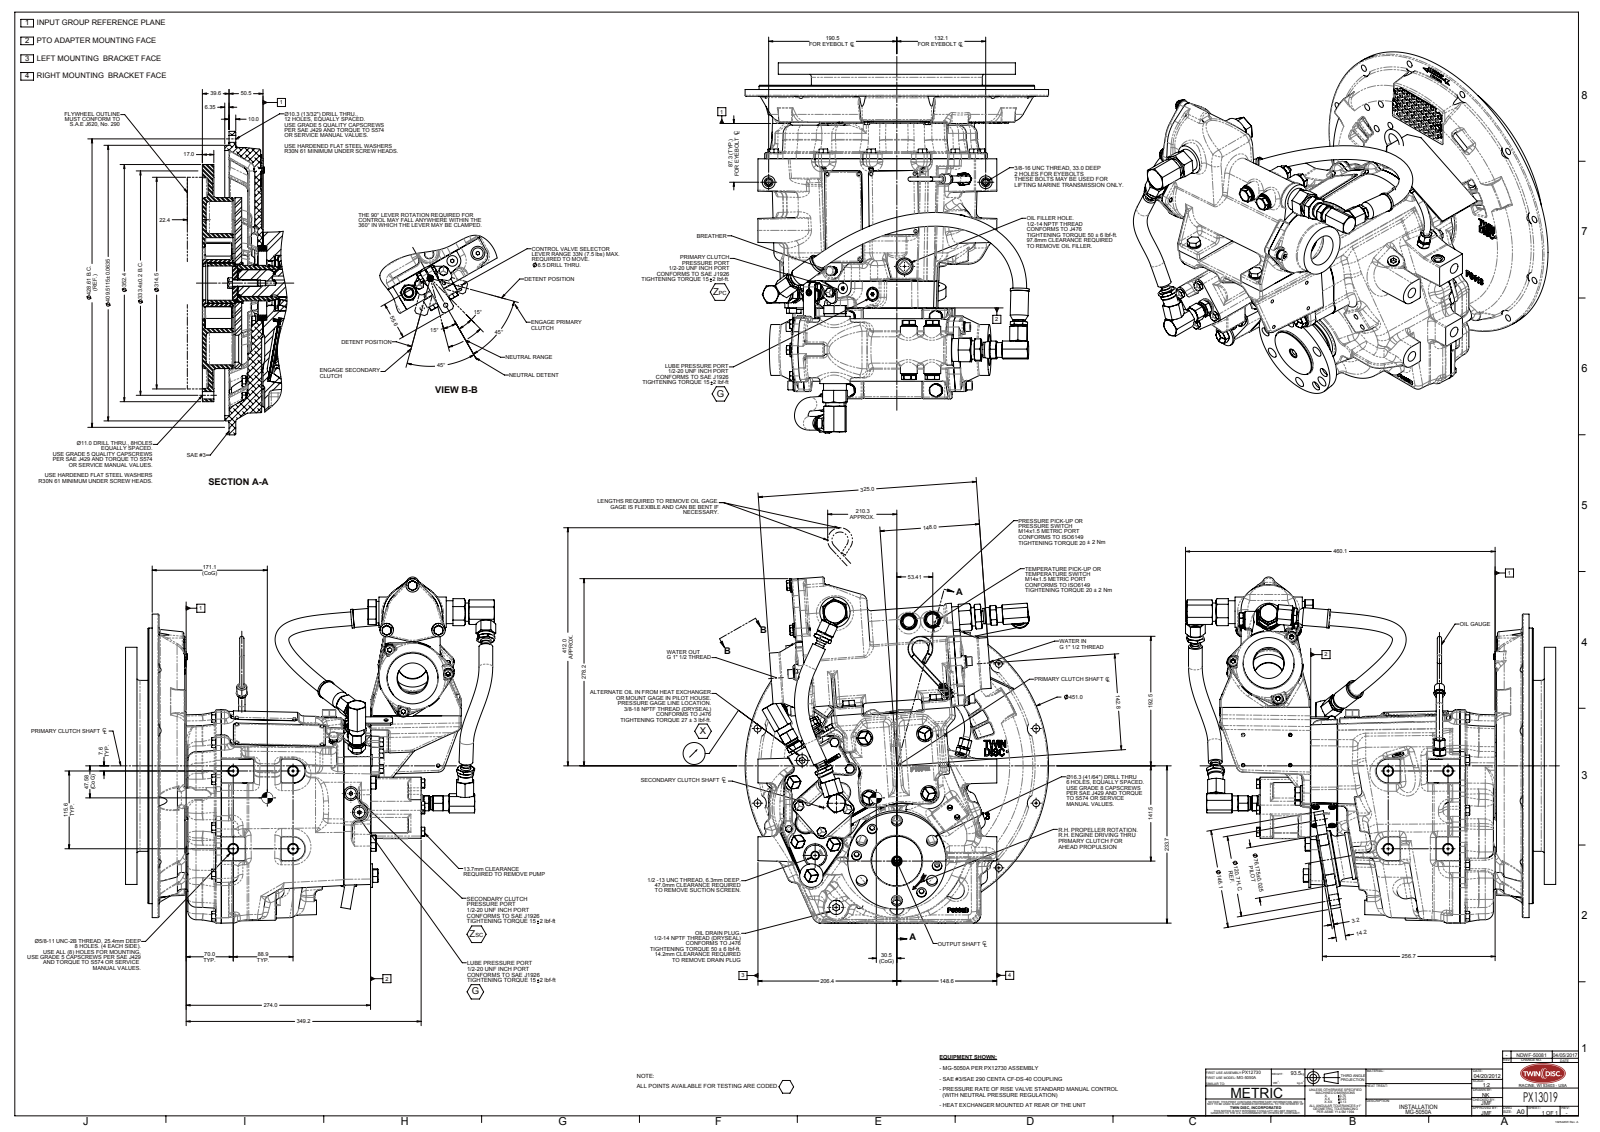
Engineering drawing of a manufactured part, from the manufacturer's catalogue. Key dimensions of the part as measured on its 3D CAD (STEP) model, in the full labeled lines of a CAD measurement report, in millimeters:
Part name (STEP PRODUCT): PX13019
STEP written by: SolidWorks 2015 (AUTOMOTIVE_DESIGN)
Units: millimetres
Bodies: 0 solids, 4454 faces (1305 planar, 1093 cylindrical, 2056 other)
Overall size (bounding box): 550.2 × 514.6 × 451
Round holes (diameter × count): ⌀7 ×51, ⌀10.3 ×15, ⌀11 ×8, ⌀8 ×7, ⌀16.3 ×6, ⌀5 ×4, ⌀6.8 ×4, ⌀7.1 ×4, ⌀10.3 ×4, ⌀14.3 ×4, ⌀20.7 ×3, ⌀9.5 ×2
Round bosses / shafts (diameter × count): ⌀32.5 ×8, ⌀16 ×8, ⌀13 ×8, ⌀24 ×6, ⌀12.5 ×6, ⌀19.8 ×4, ⌀18.9 ×4, ⌀15.9 ×4
Partial cylindrical surfaces — rounded edges, fillets, slot ends (radius × count): R1.5 ×94, R8.1 ×74, R2.5 ×67, R1.5 ×62, R8 ×52, R2 ×42, R13 ×24, R3 ×23
Main face-to-face distances: 88.1, 236, 324.1, 0.7, 236.7, 324.7, 8.5, 266.3, 265.7, 29.7
Hole centre spacings: 214.3, 214.3, 371.2, 10, 110.9, 303.1, 414, 60.3
